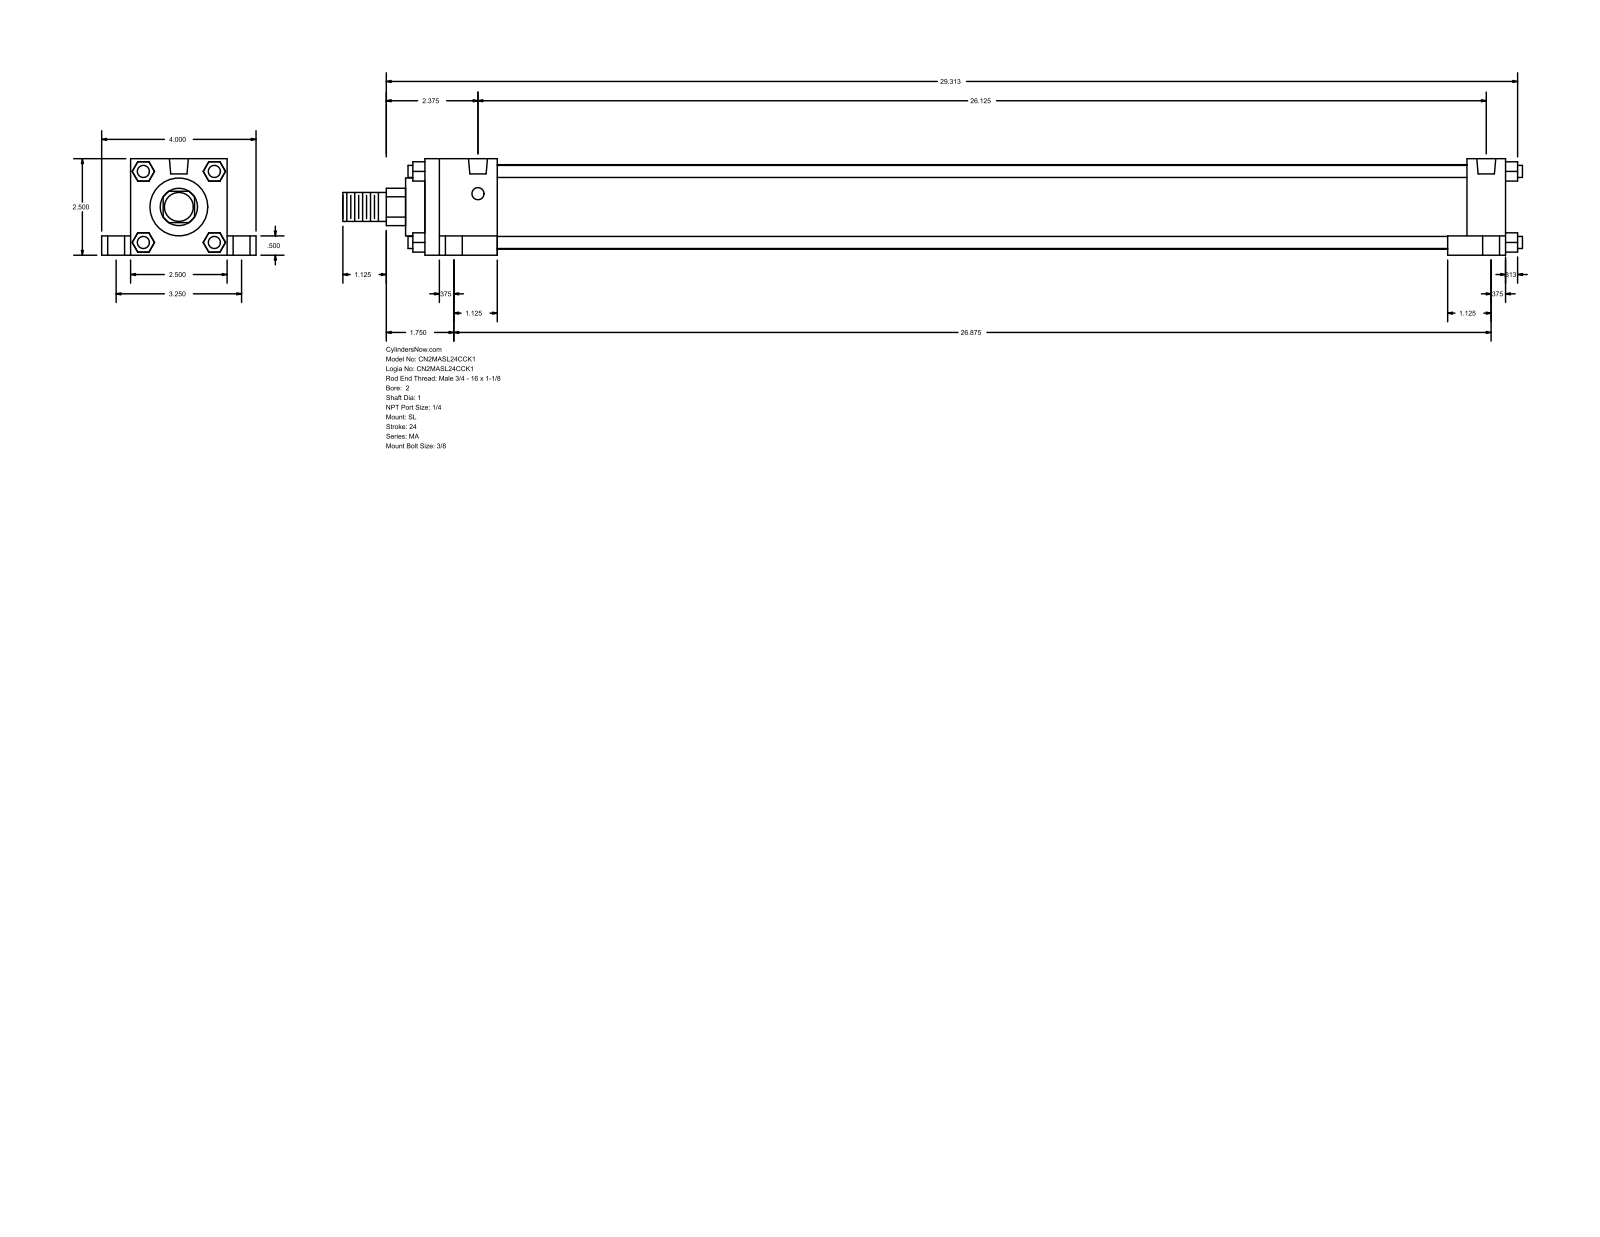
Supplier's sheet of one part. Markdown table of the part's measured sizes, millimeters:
| quantity | value |
| --- | --- |
| part name | MA_SL__0200_1 |
| STEP written by | GSSL Pune (CONFIG_CONTROL_DESIGN) |
| units | millimeters |
| bodies | 0 solids, 148 faces (112 planar, 36 cylindrical, 0 other) |
| overall size | 776.29 × 101.6 × 63.5 |
| round holes (diameter × count) | 7.94 × 4, 11.11 × 4, 17.46 × 4, 12.49 × 2 |
| round bosses / shafts (diameter × count) | 7.94 × 4, 55.63 × 1, 38.1 × 1, 25.4 × 1, 19.05 × 1 |
| partial cylindrical surfaces (radius × count) | 12.29 × 1 |
| main face-to-face distances | 63.5, 12.7, 711.2, 19.05, 82.55, 25.4, 50.8, 47.63, 663.57, 685.8 |
| hole center spacings | 41.39, 44.22, 82.54, 663.57, 668.03, 680.7, 682.63, 687.6 |
